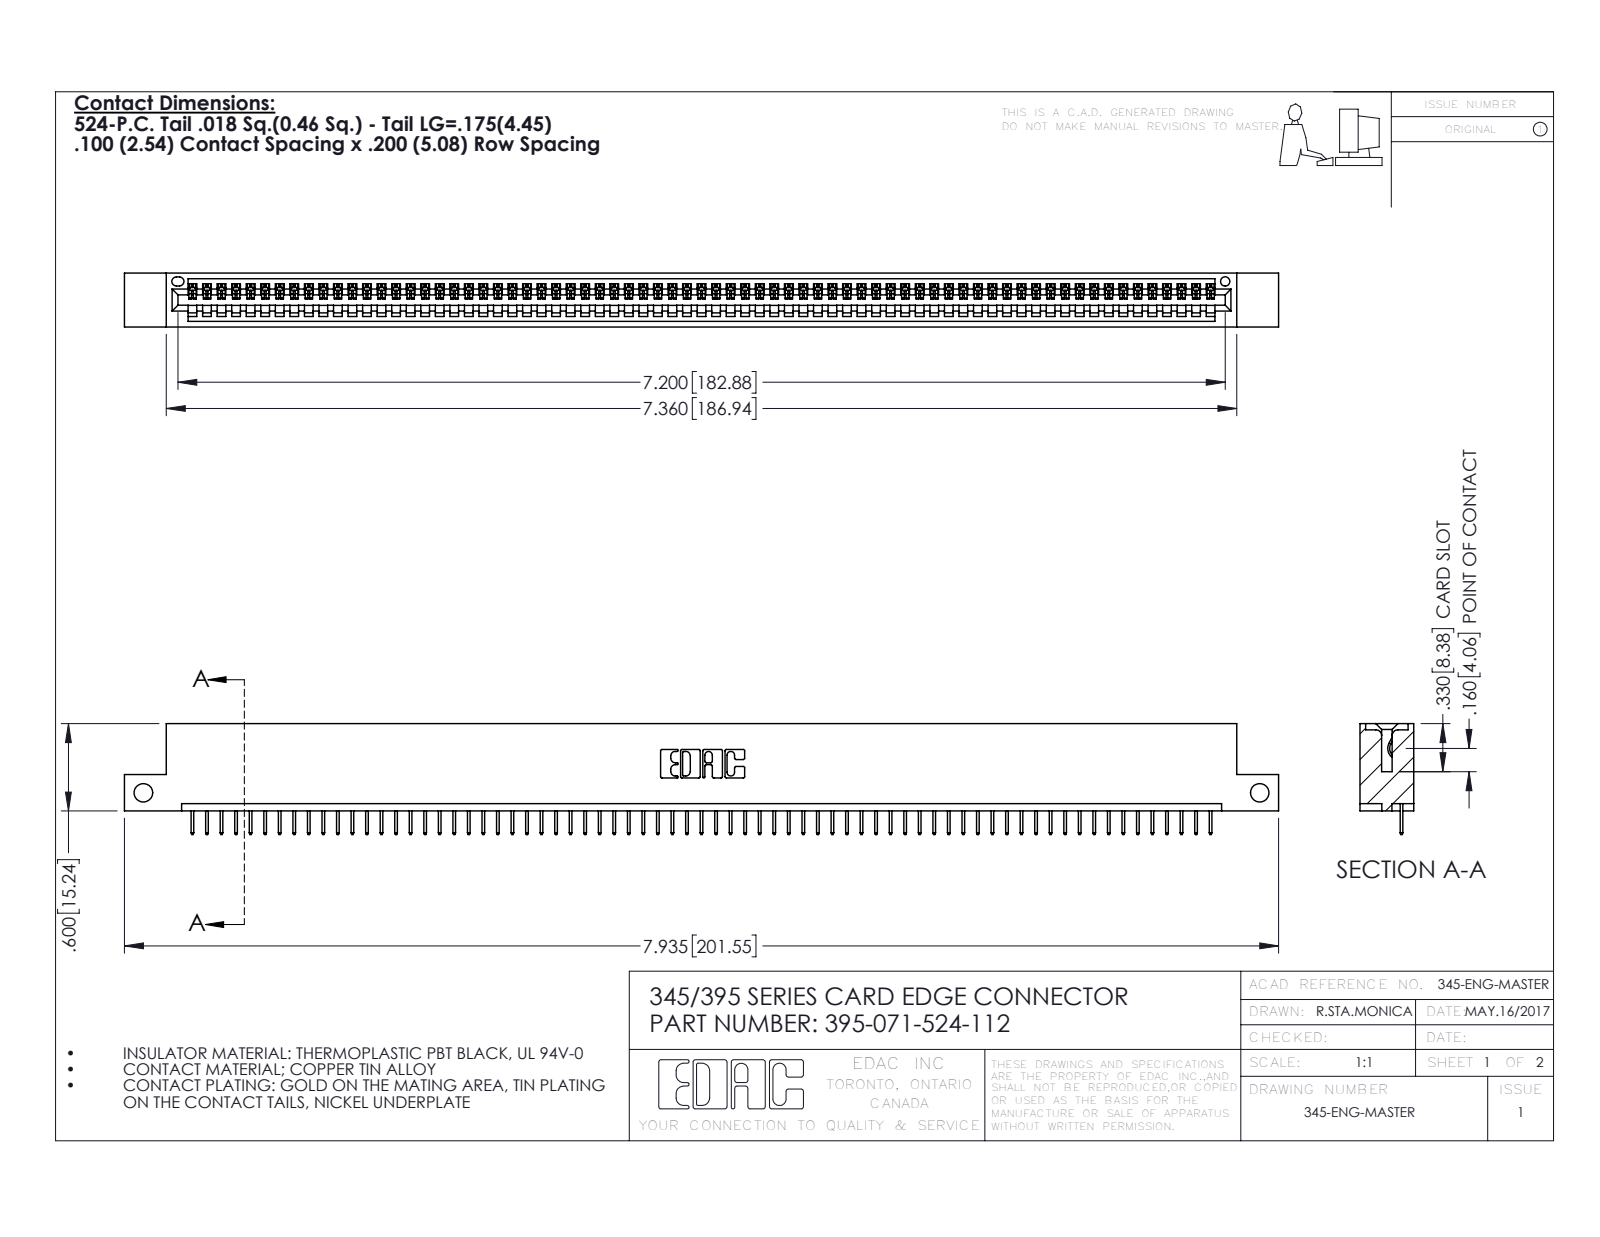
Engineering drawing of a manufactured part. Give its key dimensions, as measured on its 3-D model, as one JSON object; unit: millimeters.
{"part_name": "345 Part_Flush Mounting Lugs - Side Mount; 345-292-001_345-293-124; 395-071-524-112", "step_written_by": "SolidWorks 2016 (CONFIG_CONTROL_DESIGN)", "units": "millimeters", "bodies": {"solids": 72, "faces": 4528, "planar": 3346, "cylindrical": 1182, "other": 0}, "overall_size": [201.5, 19.4, 9.4], "volume_mm3": 19010, "surface_area_mm2": 24620, "round_holes": [[3.3, 2], [1.6, 1]], "partial_cylinders_radius": [[0.2, 142], [0.3, 22], [0.2, 6], [0.8, 6], [0.7, 3], [0.8, 2], [1, 2], [0.4, 1]], "face_to_face_distances": [7.6, 1.8, 9.4, 5.1, 2.5, 6.9, 0.6, 5.7, 1.8, 3.8], "hole_center_spacings": [194.9]}
